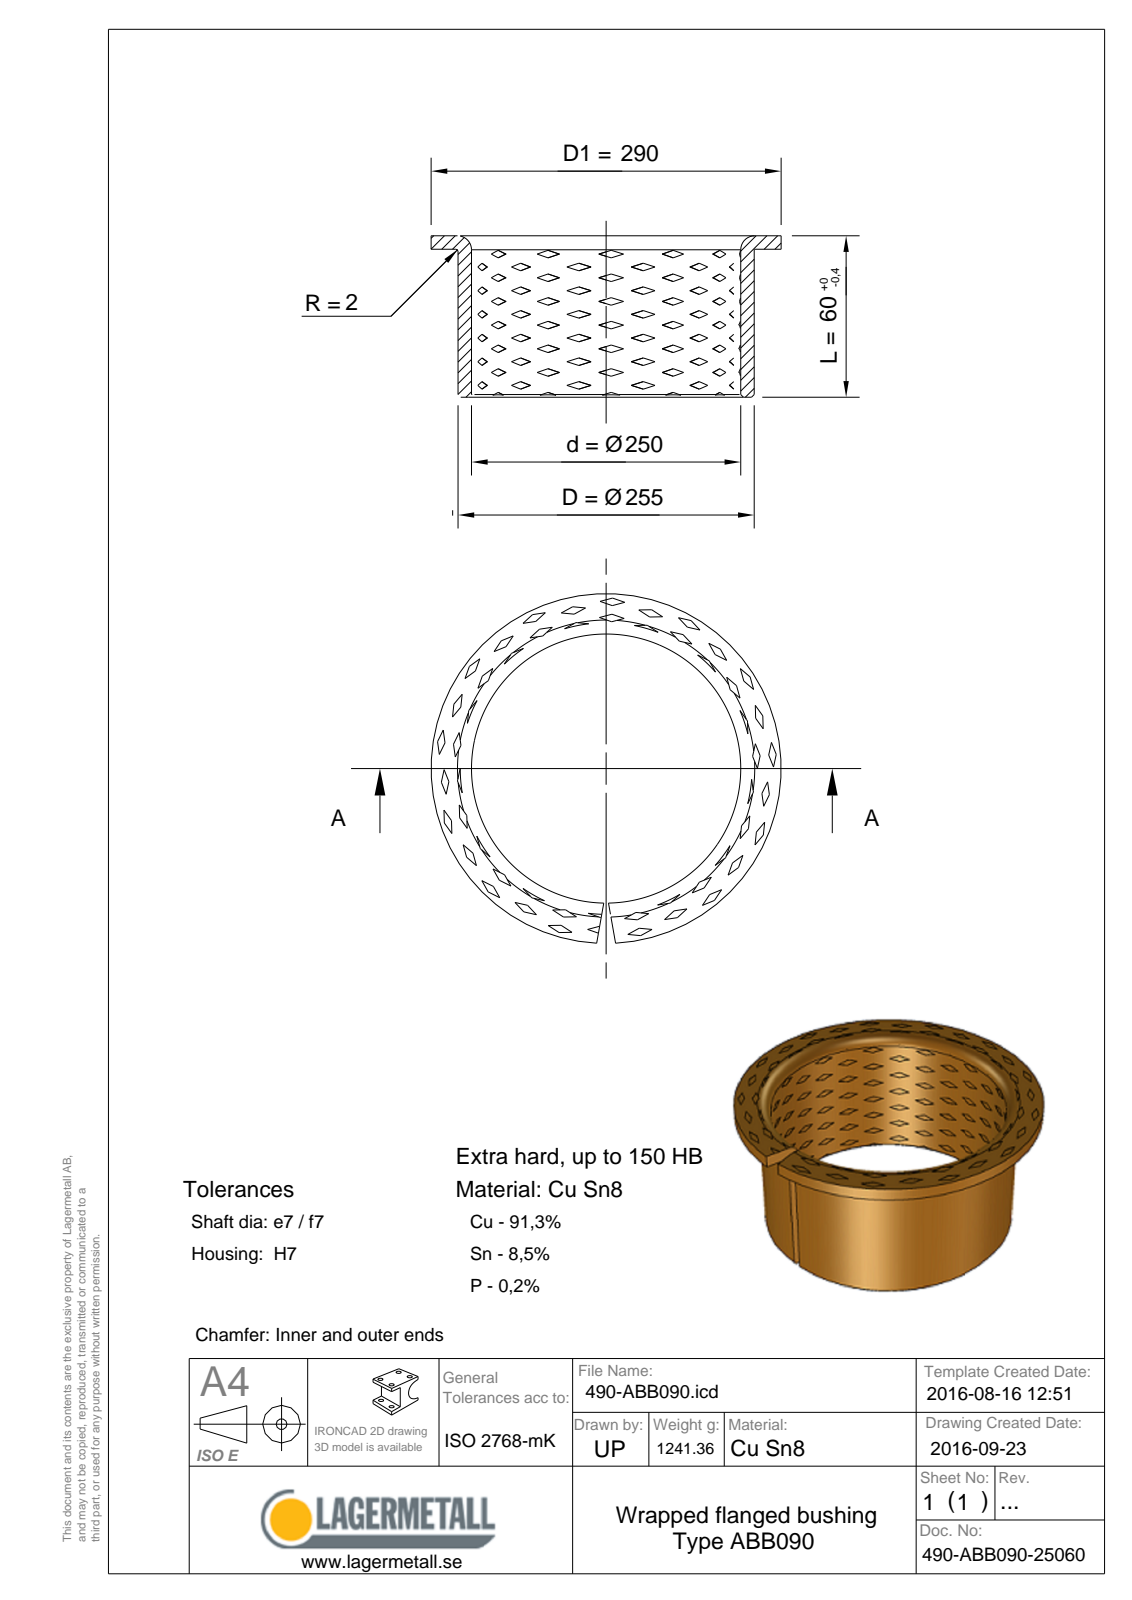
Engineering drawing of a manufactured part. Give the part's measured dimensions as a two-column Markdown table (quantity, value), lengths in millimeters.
| quantity | value |
| --- | --- |
| STEP written by | Spatial InterOp 3D (CONFIG_CONTROL_DESIGN) |
| units | millimeters |
| bodies | 1 solid, 26 faces (5 planar, 9 cylindrical, 12 other) |
| overall size | 290 × 290 × 60 |
| volume | 153 254 mm³ |
| surface area | 126 913 mm² |
| round holes (diameter × count) | 250 × 1 |
| round bosses / shafts (diameter × count) | 290 × 1, 255 × 1 |
| main face-to-face distances | 2.5, 57.5, 60 |
